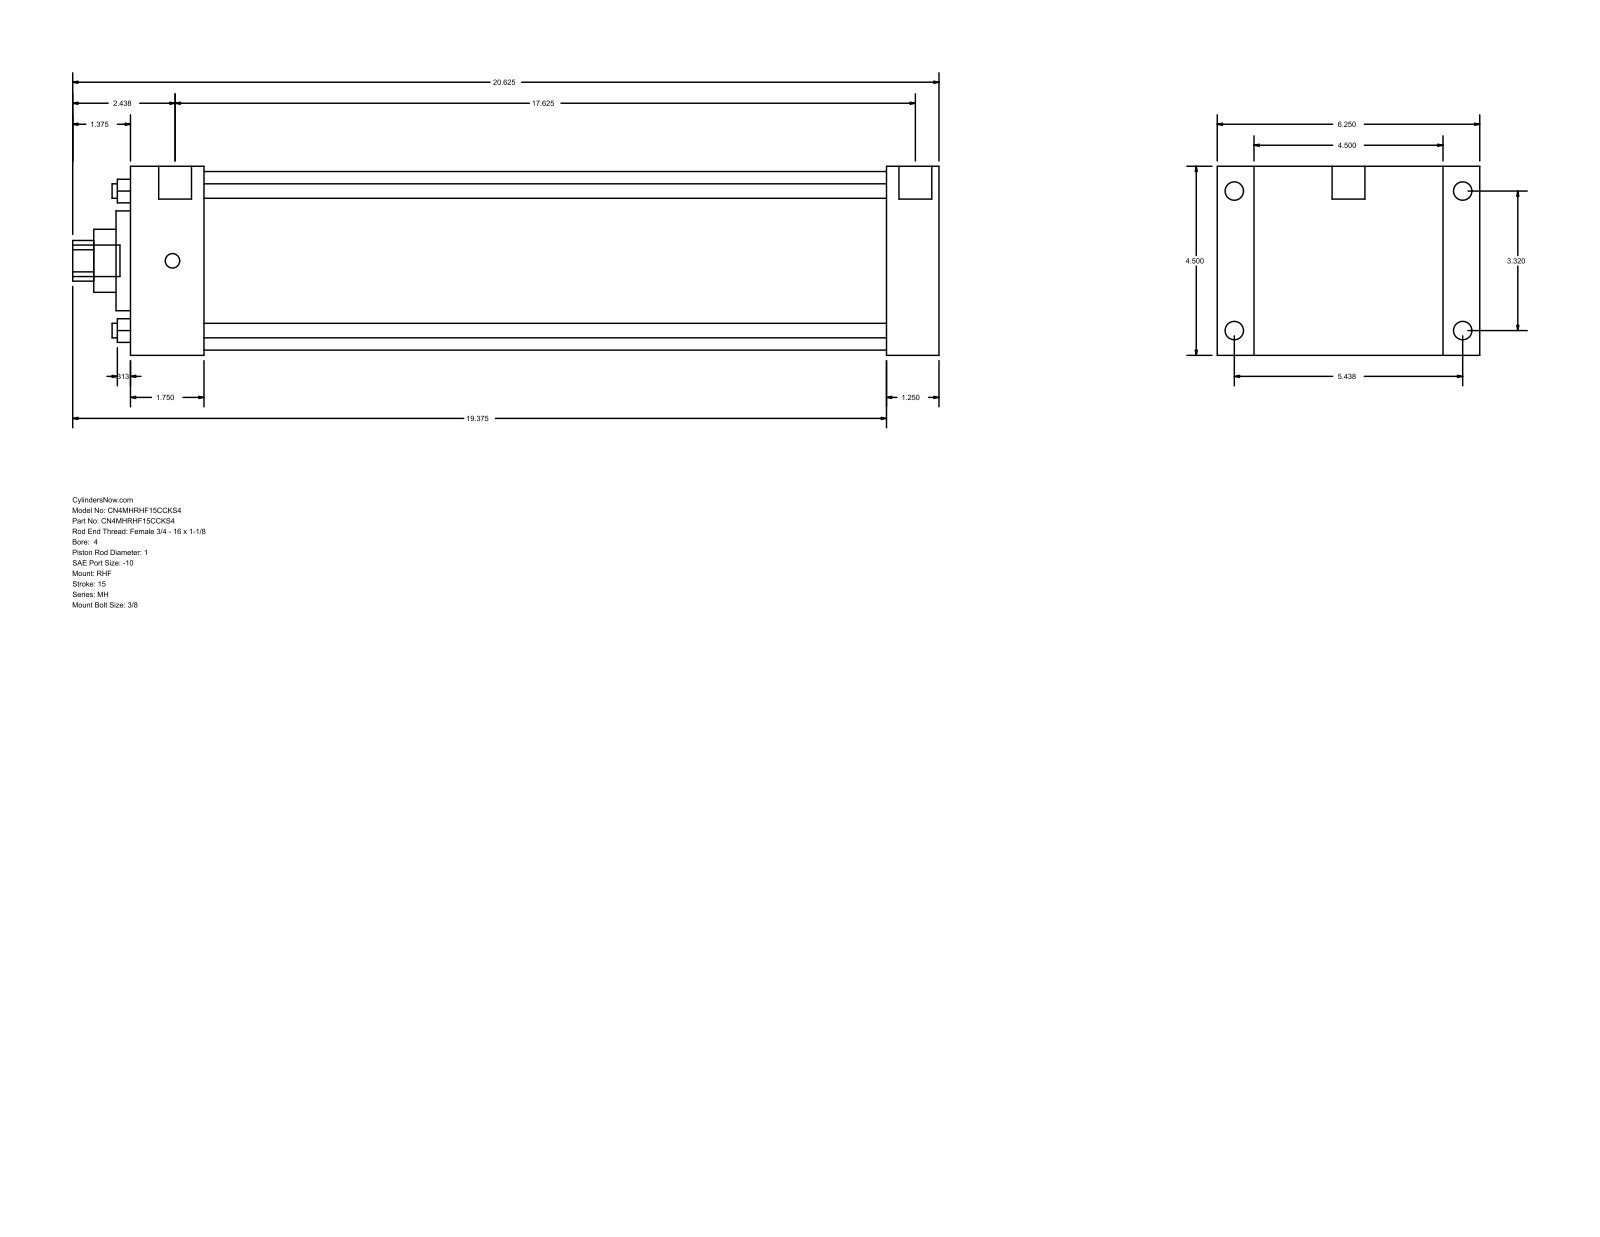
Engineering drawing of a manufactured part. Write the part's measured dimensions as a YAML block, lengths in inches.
part_name: "MH_RHF__0400_1"
step_written_by: "GSSL Pune (CONFIG_CONTROL_DESIGN)"
units: inches
bodies: {solids: 0, faces: 90, planar: 61, cylindrical: 29, other: 0}
overall_size: [20.625, 6.25, 4.5]
round_holes:
  - {diameter: 0.345, count: 4}
  - {diameter: 1, count: 1}
  - {diameter: 1.5, count: 1}
  - {diameter: 2.375, count: 1}
  - {diameter: 4.25, count: 1}
round_bosses_or_shafts:
  - {diameter: 0.438, count: 4}
  - {diameter: 0.344, count: 4}
  - {diameter: 0.781, count: 2}
  - {diameter: 0.75, count: 1}
partial_cylinders:
  - {radius: 0.484, count: 1}
face_to_face_distances: [4.5, 19.25, 18, 1.25, 0.875, 5.375, 1.75, 16.25, 17.5, 6.25]
hole_center_spacings: [2.347, 3.32, 4.695]
